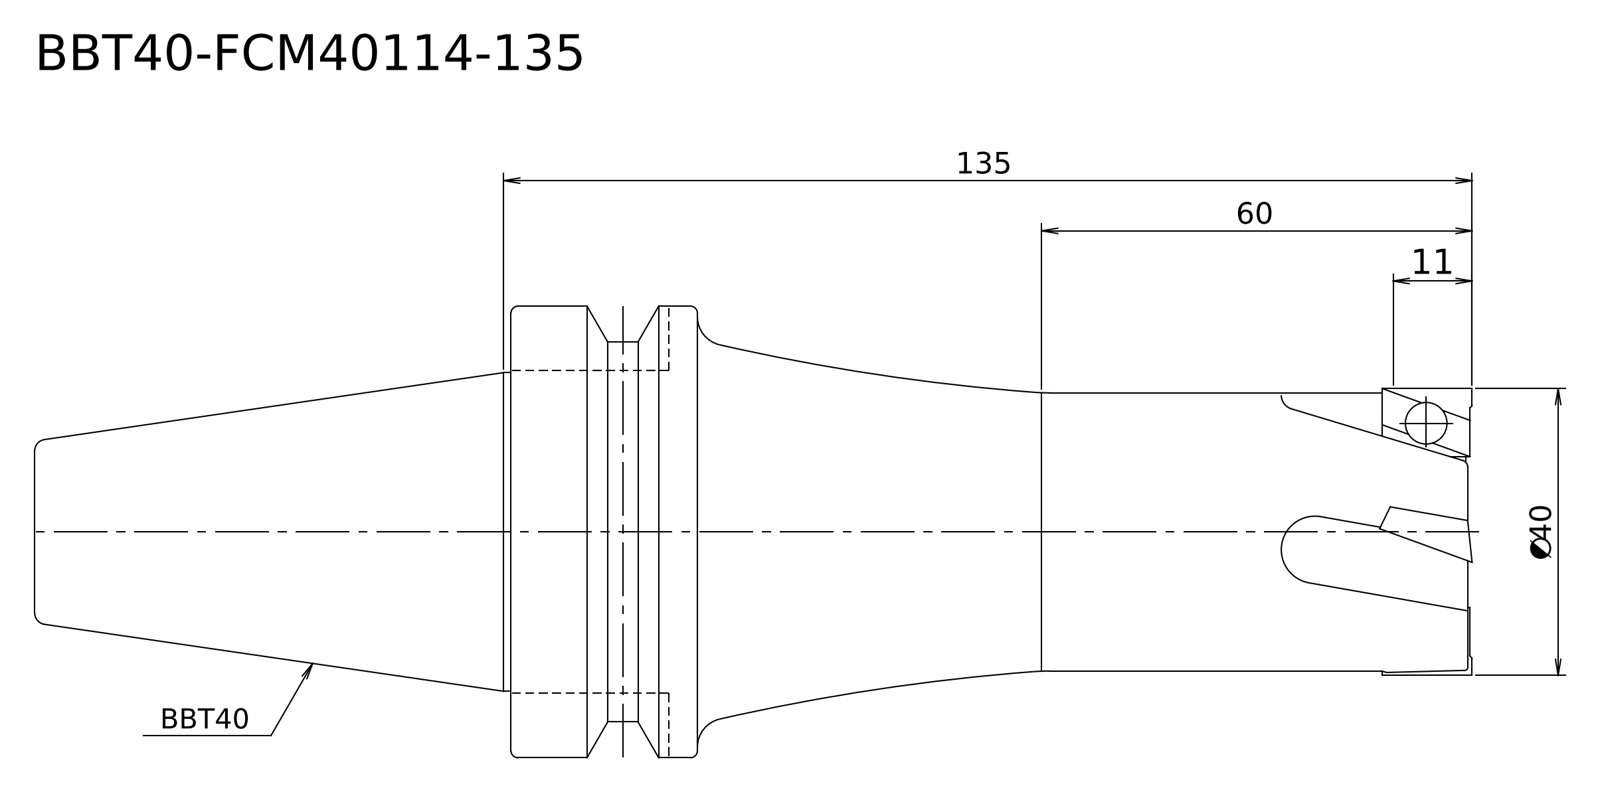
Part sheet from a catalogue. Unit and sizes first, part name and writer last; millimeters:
Units: millimetres
Overall size (bounding box): 200.4 × 63 × 63
Round bosses / shafts (diameter × count): ⌀63 ×1, ⌀53 ×1, ⌀44.45 ×1, ⌀40 ×1, ⌀38.8 ×1
Main face-to-face distances: 134, 200.4, 66.4, 108, 26, 92.4
Volume: 292 986 mm³ · Surface area: 31 707 mm²
Bodies: 1 solid, 17 faces (4 planar, 6 cylindrical, 7 other)
STEP written by: Kubotek KeyCreator V8.5.1 (14335) (CONFIG_CONTROL_DESIGN)
